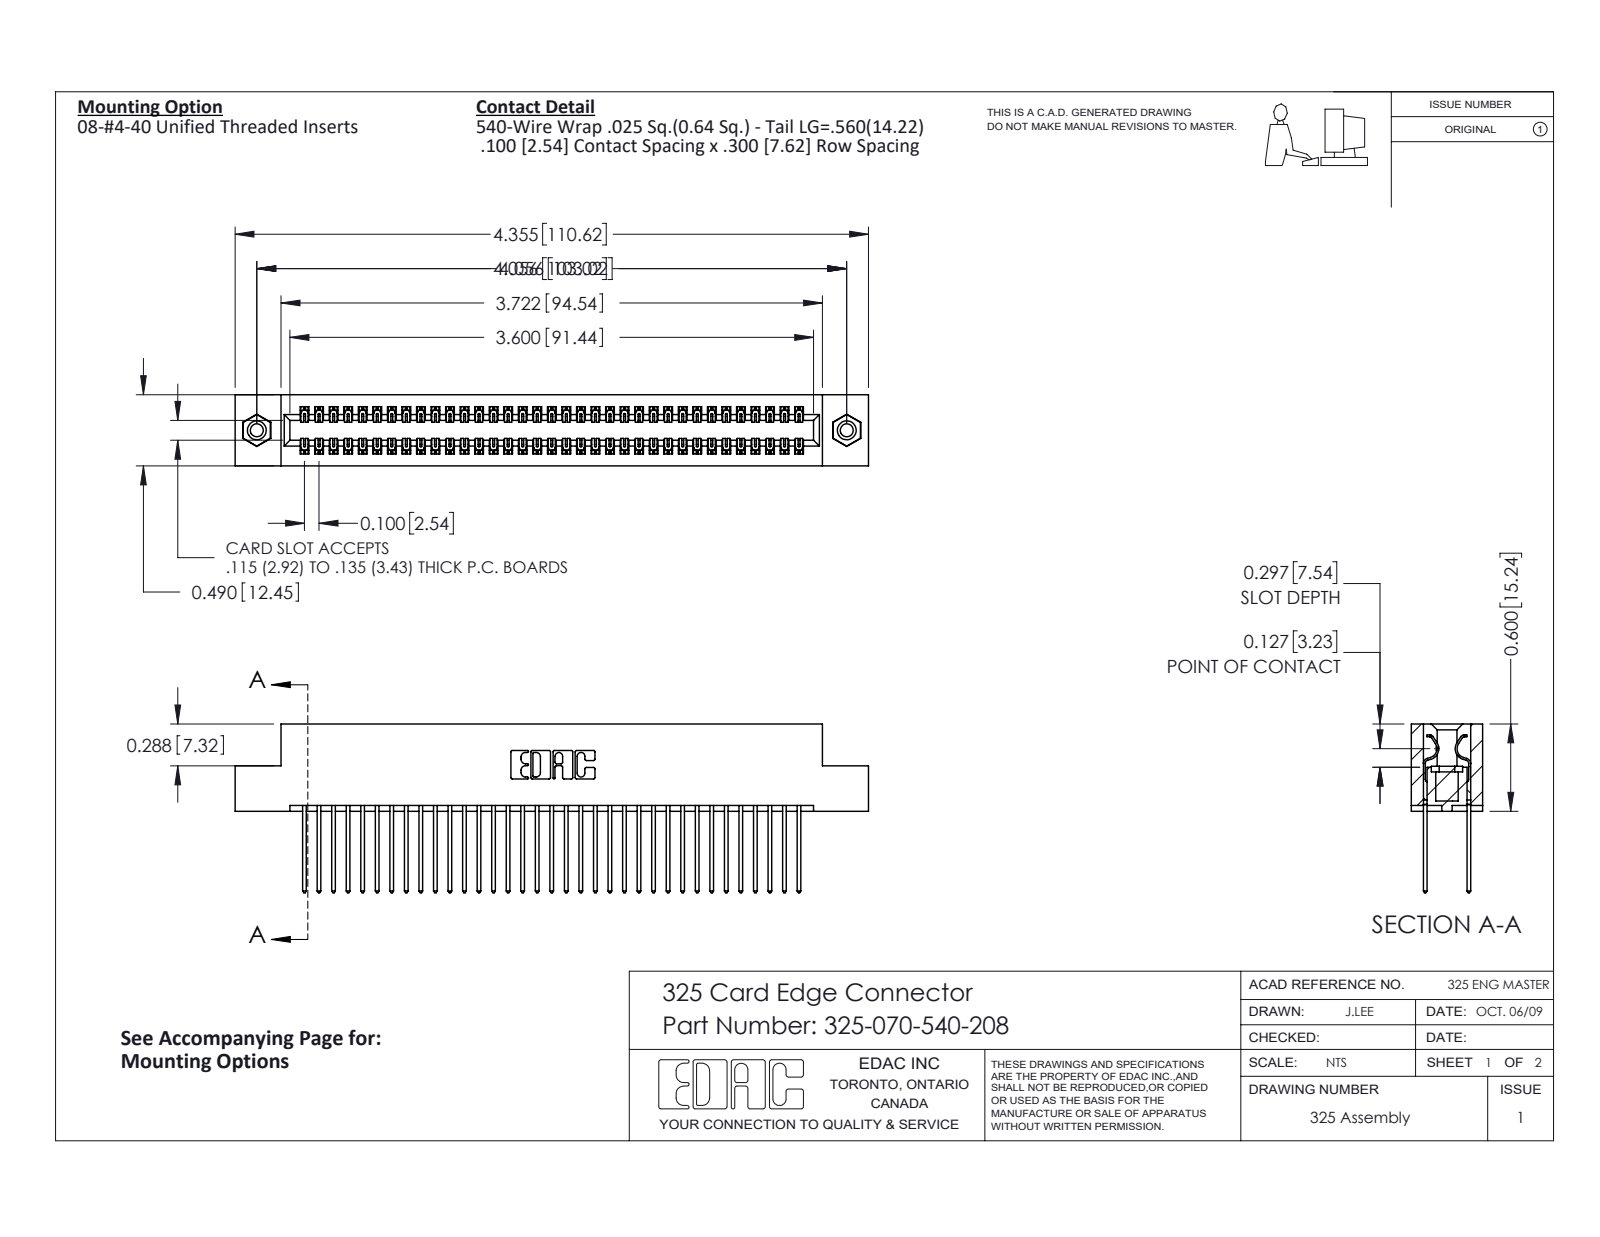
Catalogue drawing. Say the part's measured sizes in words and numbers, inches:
The part is named "345-250-001_345-250-003-102; 325-070-540-208; 325 Part_TI; 325-292-001_325-293-140". Its 3-D file was written by "SolidWorks 2016 (CONFIG_CONTROL_DESIGN)". It is 73 solids with 3814 faces: 2622 planar, 1176 cylindrical and 16 other. Overall it measures 4.355 by 1.16 by 0.49 inches. Its volume is 0.883 cubic inches and its surface area 28.88 square inches. Round holes: 2 of diameter 0.089, 2 of diameter 0.125, 2 of diameter 0.16. Round bosses or shafts: 2 of diameter 0.155. Partial cylindrical surfaces (rounded edges, fillets, slot ends): 105 of radius 0.006, 70 of radius 0.01, 22 of radius 0.01, 6 of radius 0.007, 6 of radius 0.031, 3 of radius 0.026, 2 of radius 0.014, 2 of radius 0.022. The main face-to-face distances are 0.083, 0.407, 0.3, 0.107, 0.383, 0.025, 0.49, 0.325, 0.275, 0.56. The hole center spacings are 4.056.
